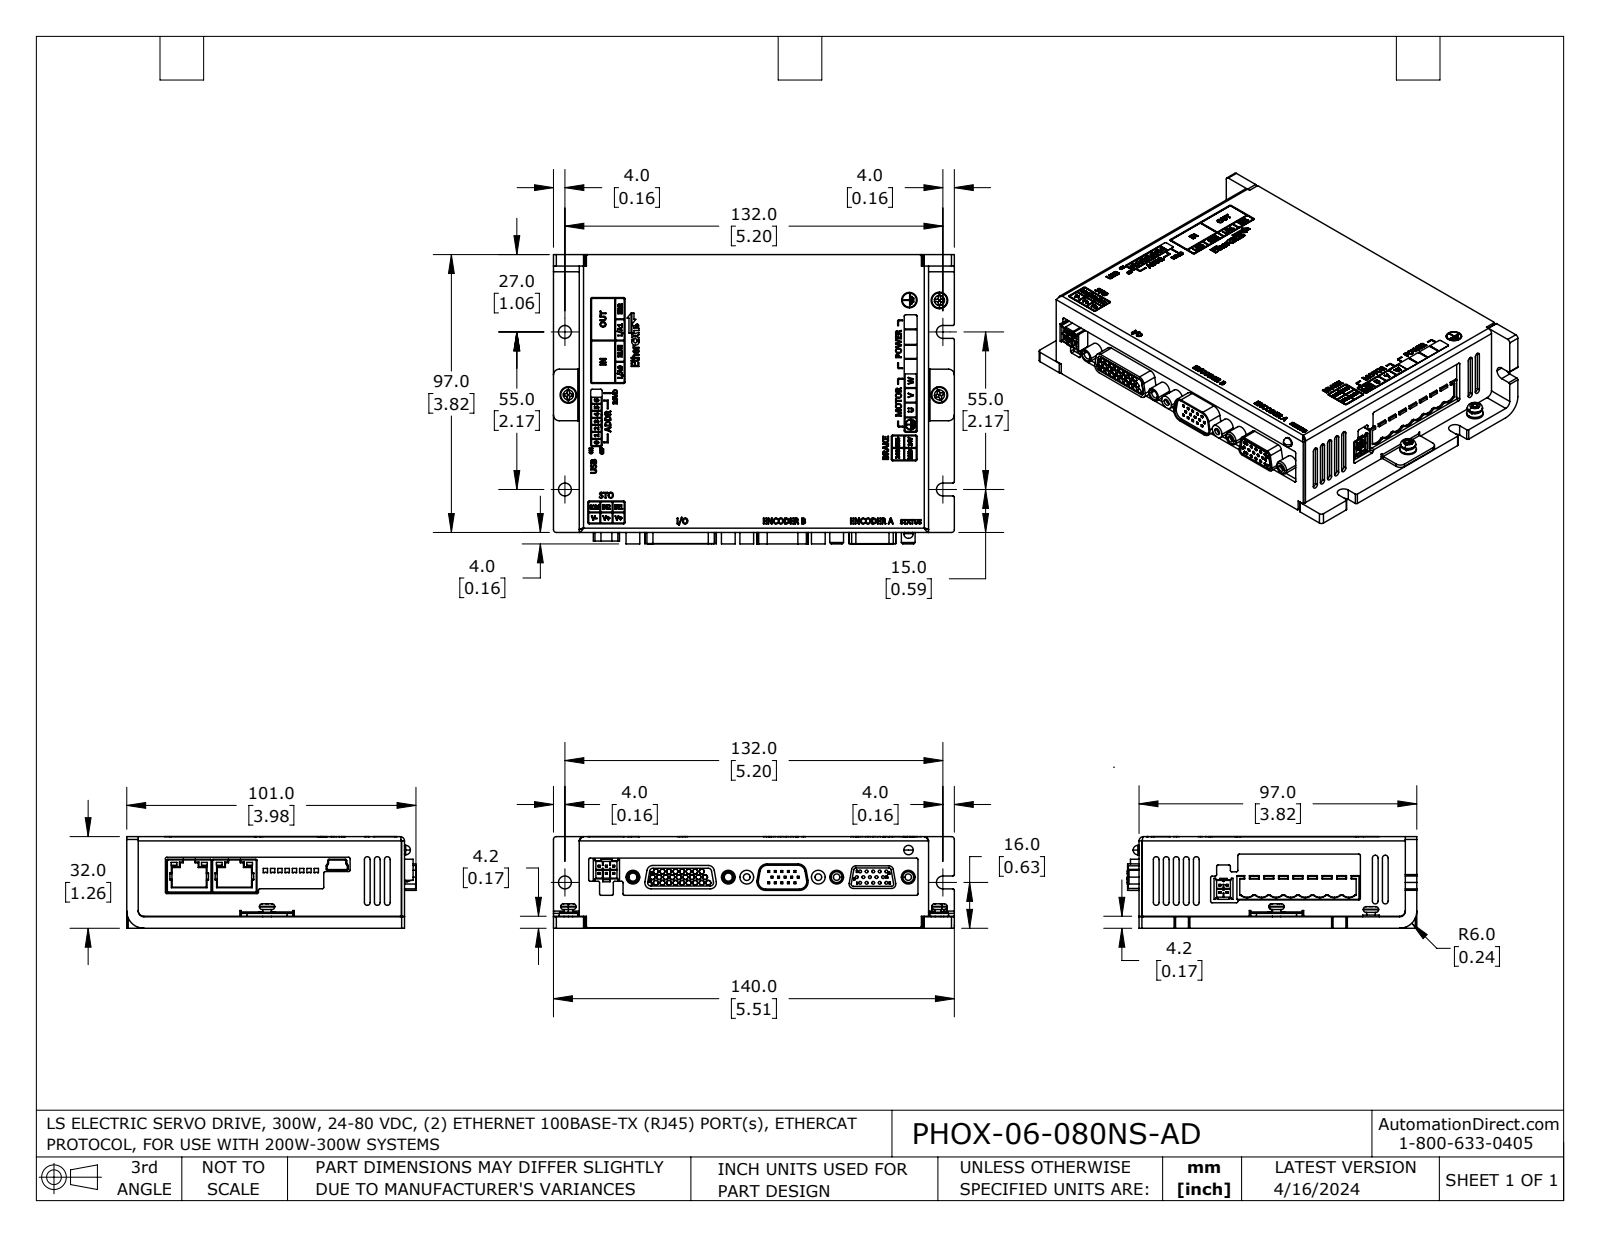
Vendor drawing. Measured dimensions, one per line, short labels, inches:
name: PHOX-06-080NS-AD
written by: SolidWorks 2021 (AUTOMOTIVE_DESIGN)
unit: in
bodies: 4 solids, 3941 faces (2416 planar, 365 cylindrical, 1160 other)
size: 5.512 × 3.978 × 1.26
volume: 23.54 in³; area: 73.64 in²
holes: 15× ⌀0.039, 3× ⌀0.098, 3× ⌀0.177, 2× ⌀0.089, 2× ⌀0.093, 2× ⌀0.112, 2× ⌀0.144, 1× ⌀0.036, 1× ⌀0.13, 1× ⌀0.193
bosses: 6× ⌀0.189, 3× ⌀0.228, 3× ⌀0.209, 3× ⌀0.118, 1× ⌀0.213, 1× ⌀0.146, 1× ⌀0.13, 1× ⌀0.044
rounds: 91× R0.02, 22× R0.008, 18× R0.039, 12× R0.035, 9× R0.01, 9× R0.059, 8× R0.03, 6× R0.079
face distances: 1.26, 0.157, 3.819, 0.059, 1.102, 4.803, 4.744, 0.039, 0.354, 0.413
hole spacings: 0.09, 0.238, 0.156, 0.09, 0.18, 0.325, 0.18, 0.156
